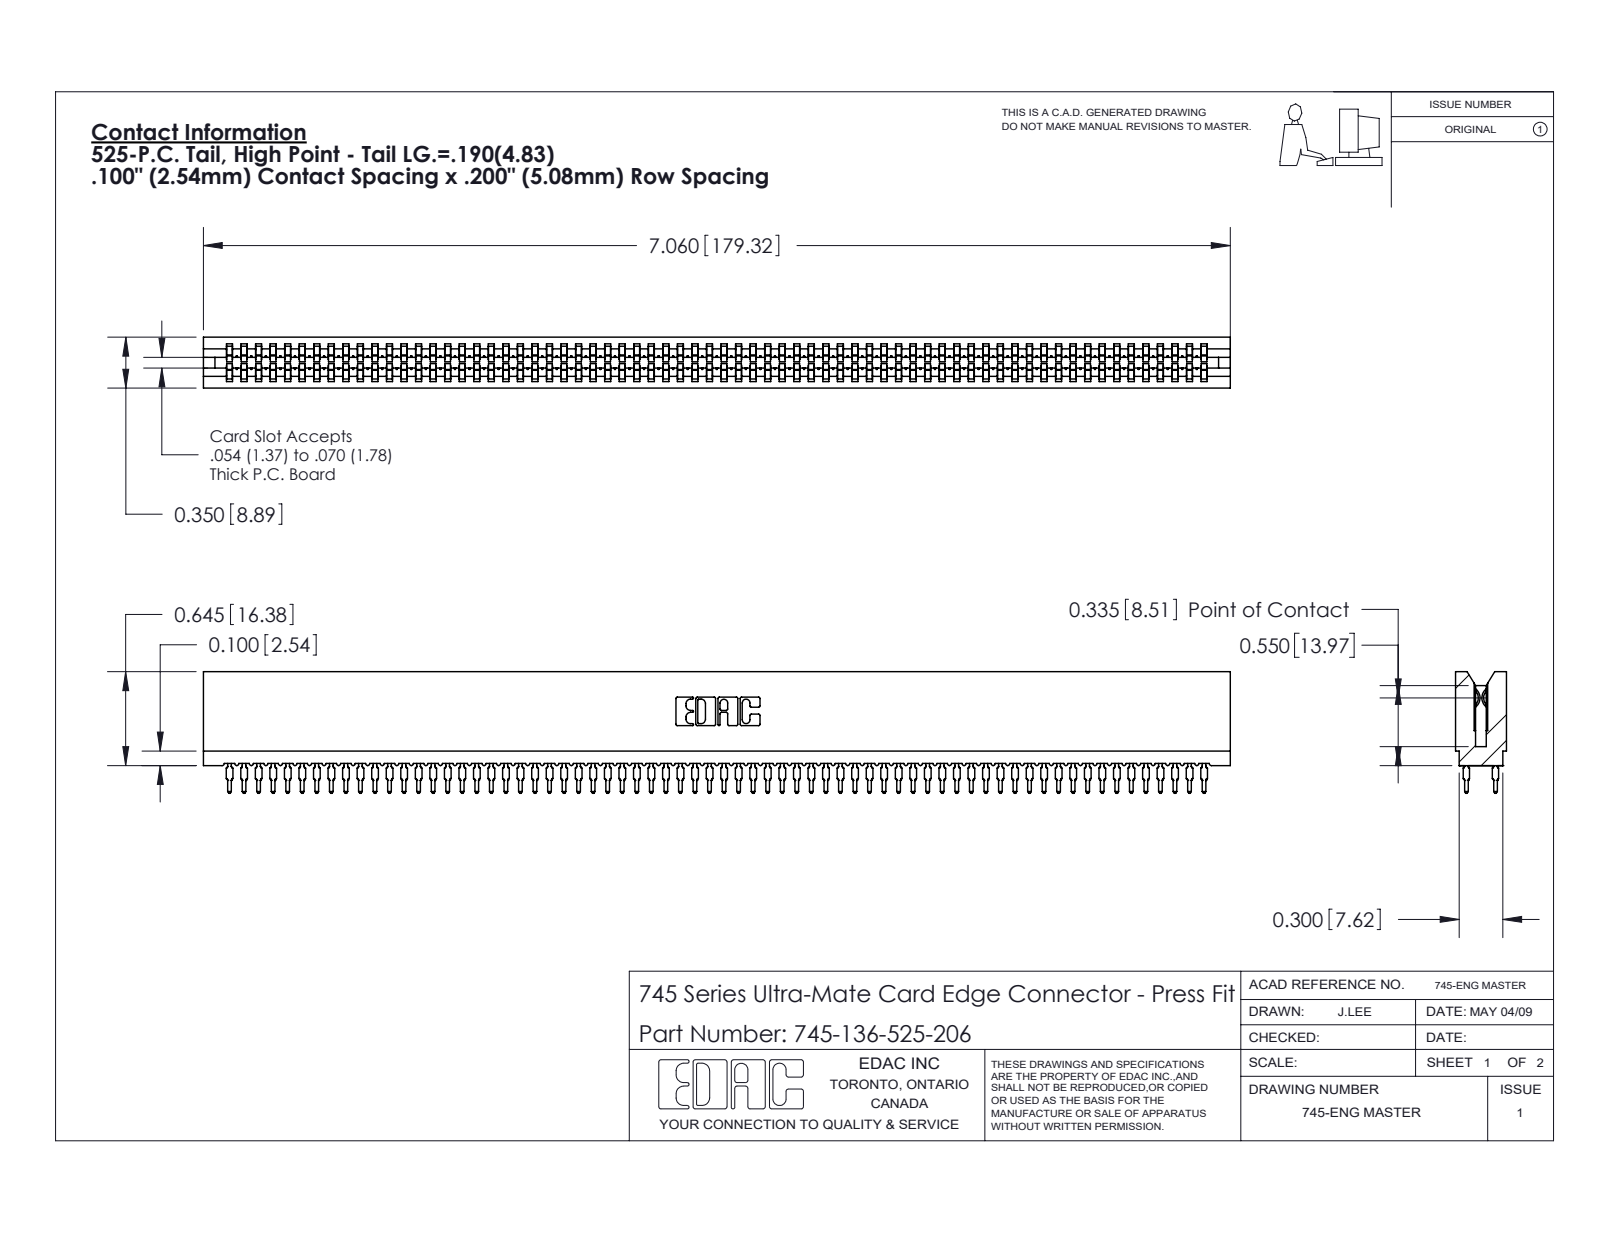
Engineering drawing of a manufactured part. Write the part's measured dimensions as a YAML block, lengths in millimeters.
part_name: "745-136-525-206; 745-292-001_525; 745 Part_Insulator Option - 06"
step_written_by: "SolidWorks 2020 (CONFIG_CONTROL_DESIGN)"
units: millimeters
bodies: {solids: 137, faces: 12268, planar: 6312, cylindrical: 2420, other: 3536}
overall_size: [179.3, 21.2, 8.9]
volume: 15900
surface_area: 32890
partial_cylinders:
  - {radius: 0.5, count: 272}
  - {radius: 0.4, count: 136}
  - {radius: 0.3, count: 22}
  - {radius: 0.1, count: 8}
  - {radius: 0.3, count: 8}
  - {radius: 0.2, count: 6}
  - {radius: 0.8, count: 6}
  - {radius: 0.7, count: 3}
face_to_face_distances: [8.9, 1.6, 7.3, 1.1, 7.7, 0.5, 6.2, 3.5, 5.4, 2.4]
